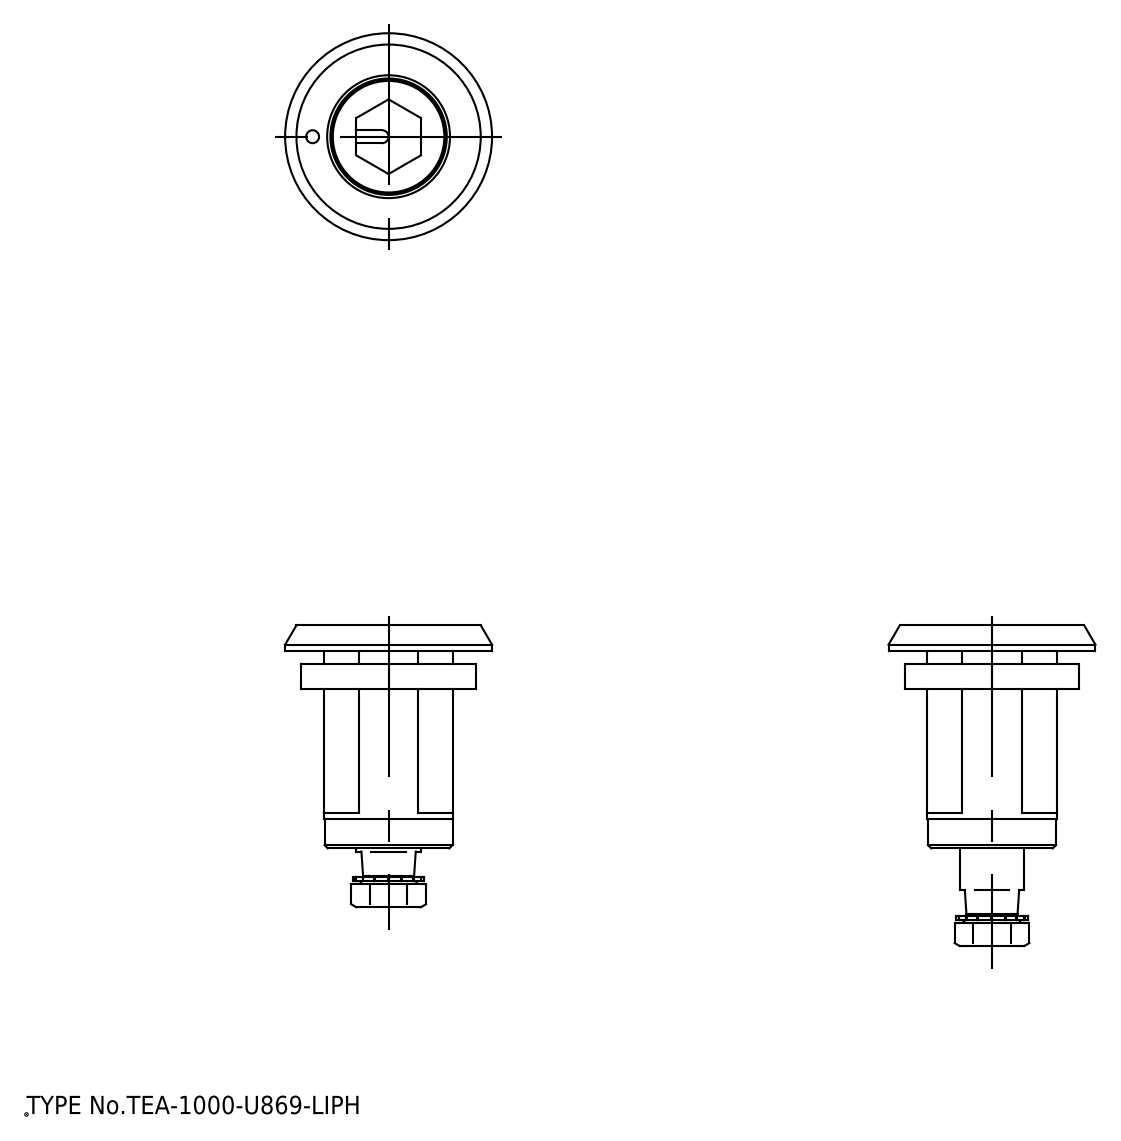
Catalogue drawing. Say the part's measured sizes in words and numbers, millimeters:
The part is named "1000-000530-00000VA_00753127; 1000-000532-00002VA_00804780; 1000-000531-00000VA_00753129; 1000-02 (+2 more)". Its 3-D file was written by "spGate 17.5.1 (AUTOMOTIVE_DESIGN)". It is 6 solids with 378 faces: 220 planar, 91 cylindrical and 67 other. Overall it measures 43.6 by 32 by 32 millimeters. Its volume is 11 946 cubic millimeters and its surface area 11 571 square millimeters. Round holes: 2 of diameter 4, 2 of diameter 5, 1 of diameter 3.6, 1 of diameter 6.2, 1 of diameter 6.4, 1 of diameter 10, 1 of diameter 17.6, 1 of diameter 18, 1 of diameter 20.38, 1 of diameter 29.5. Round bosses or shafts: 1 of diameter 32, 1 of diameter 23.5, 1 of diameter 19.8, 1 of diameter 17.25, 1 of diameter 13.4, 1 of diameter 11, 1 of diameter 9.95, 1 of diameter 6. Partial cylindrical surfaces (rounded edges, fillets, slot ends): 12 of radius 0.3, 5 of radius 0.2, 5 of radius 1, 2 of radius 0.7, 1 of radius 11. The main face-to-face distances are 2, 4, 27, 6, 20, 3.5, 5, 3.8, 9.8, 21. The hole center spacings are 7.
